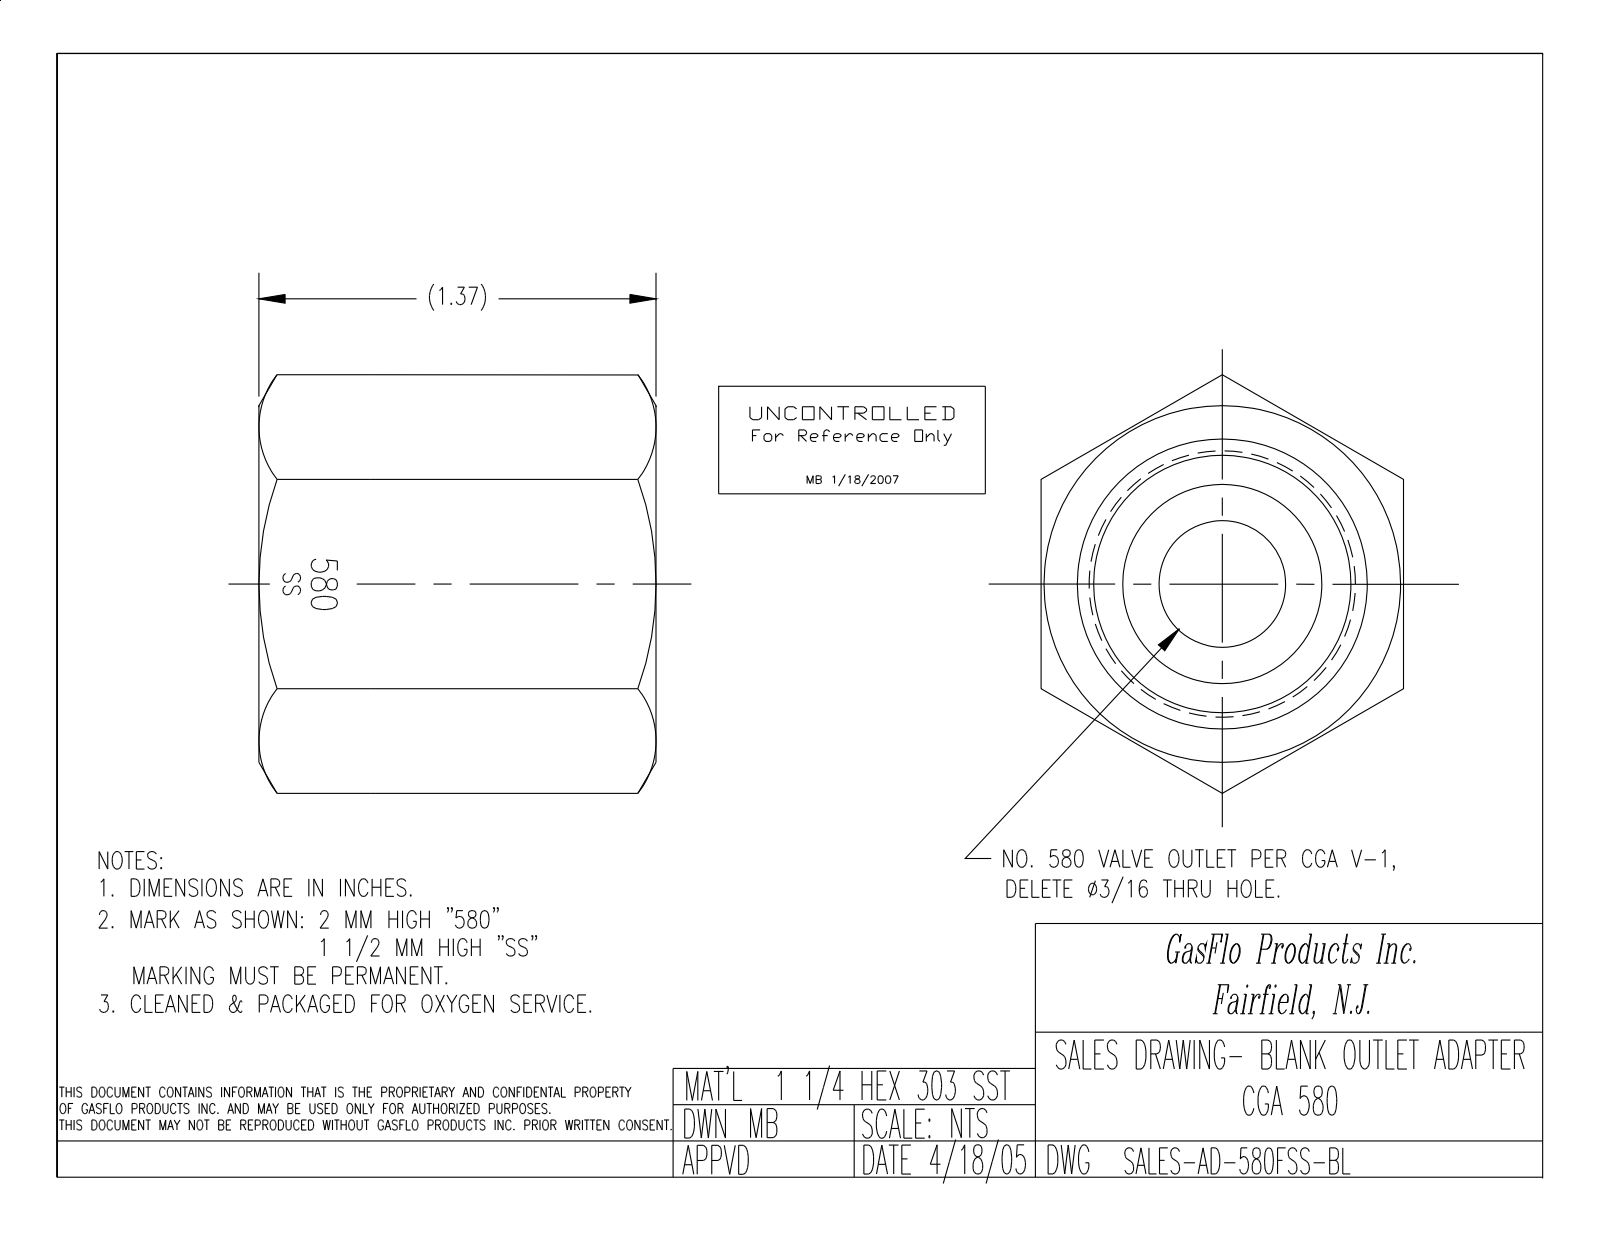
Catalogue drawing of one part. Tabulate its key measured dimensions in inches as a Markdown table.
| quantity | value |
| --- | --- |
| part name | AD-580FSS-BL |
| STEP written by | SolidWorks 2012 (AUTOMOTIVE_DESIGN) |
| units | inches |
| bodies | 1 solid, 123 faces (27 planar, 18 cylindrical, 78 other) |
| overall size | 1.443 × 1.37 × 1.25 |
| volume | 1.311 in³ |
| surface area | 11.92 in² |
| round holes (diameter × count) | 0.422 × 1, 0.892 × 1 |
| main face-to-face distances | 1.25, 1.25, 1.37, 0.683, 0.687, 1.24, 0.3, 0.383, 1.07, 0.29 |
